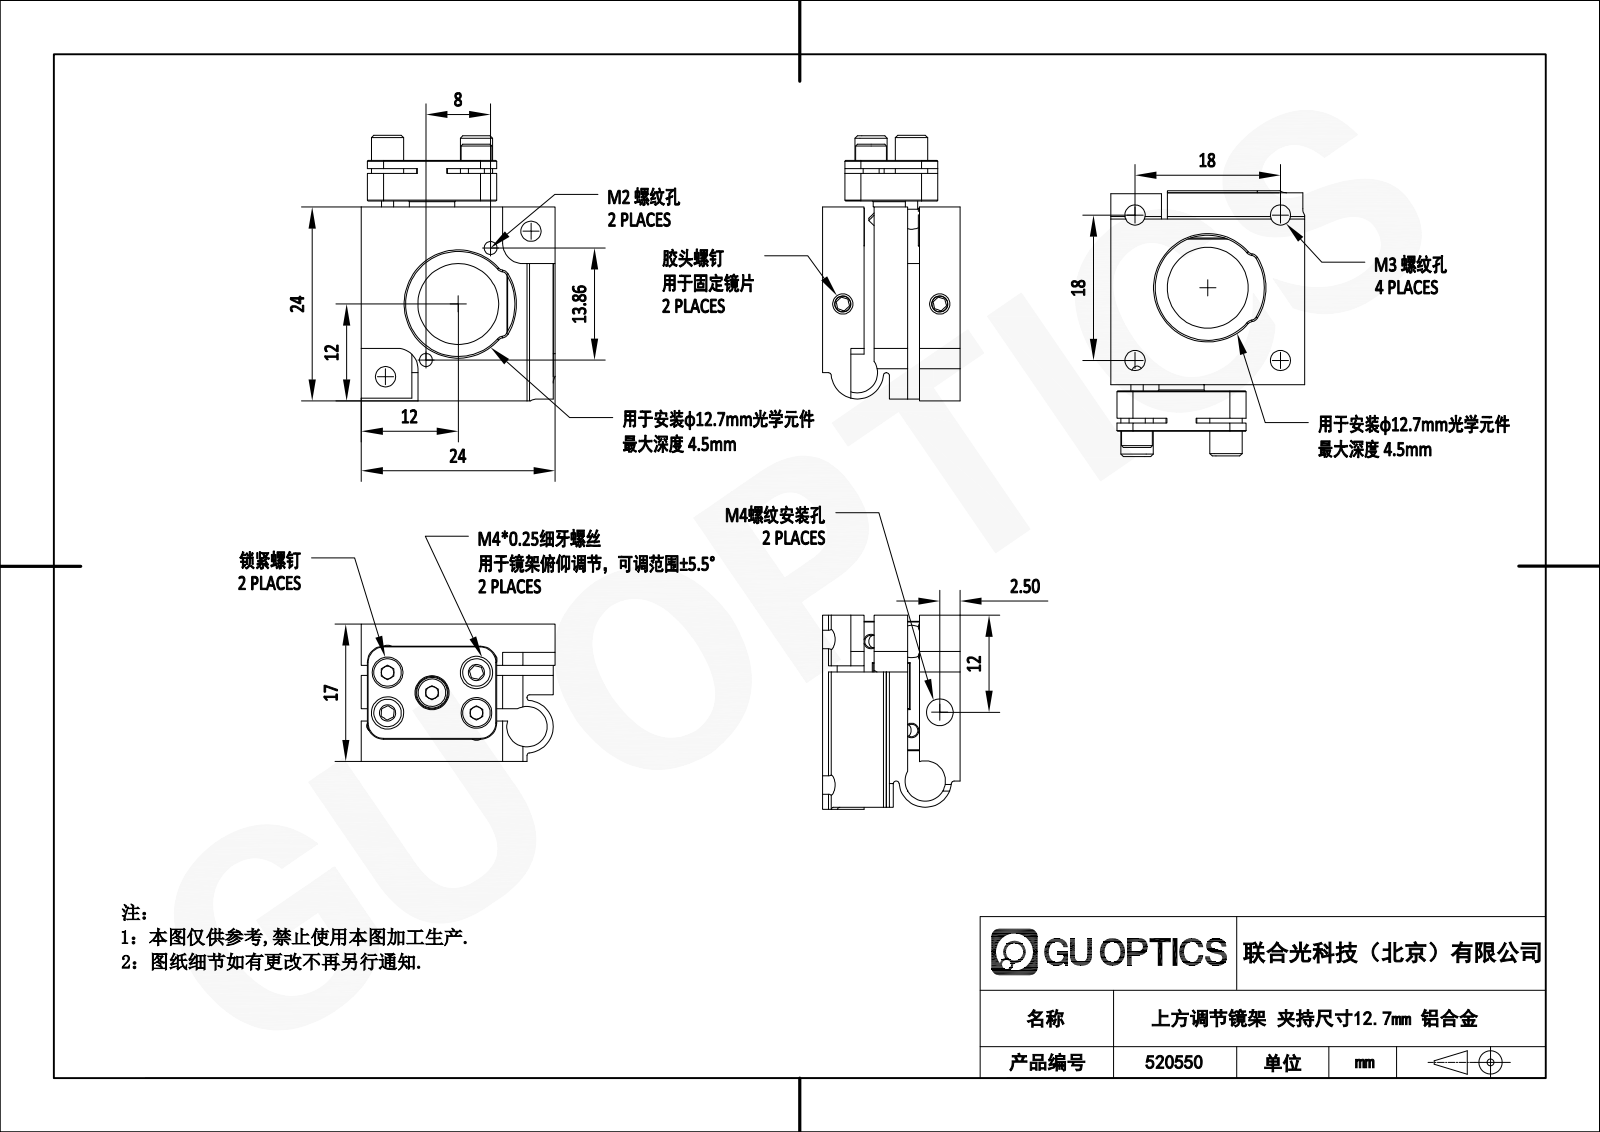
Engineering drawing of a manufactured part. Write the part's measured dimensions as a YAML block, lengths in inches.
part_name: "耳1.5 440C粣創詩埴翐种_33.2.25-DZ-耳1.5*5; 1.1.6.1.3_标准挠性光学调整架M4x0.25细牙螺丝，长度8mm，零部件; 30.1.圆柱头内六角不锈钢螺丝_30.1.18-M2*6; 30.1.圆柱头内六角不锈钢螺丝_30.1.16-M2*4 (+2 more)"
step_written_by: "SolidWorks 2021 (CONFIG_CONTROL_DESIGN)"
units: inches
bodies: {solids: 16, faces: 469, planar: 173, cylindrical: 168, other: 128}
overall_size: [1.294, 0.945, 0.63]
volume: 0.309
surface_area: 10.33
round_holes:
  - {diameter: 0.098, count: 6}
  - {diameter: 0.13, count: 4}
  - {diameter: 0.063, count: 3}
  - {diameter: 0.059, count: 2}
  - {diameter: 0.081, count: 2}
  - {diameter: 0.083, count: 2}
  - {diameter: 0.118, count: 2}
  - {diameter: 0.197, count: 2}
  - {diameter: 0.087, count: 1}
  - {diameter: 0.157, count: 1}
  - {diameter: 0.394, count: 1}
round_bosses_or_shafts:
  - {diameter: 0.079, count: 5}
  - {diameter: 0.059, count: 5}
  - {diameter: 0.15, count: 3}
  - {diameter: 0.157, count: 2}
  - {diameter: 0.118, count: 2}
partial_cylinders:
  - {radius: 0.014, count: 6}
  - {radius: 0.079, count: 6}
  - {radius: 0.03, count: 5}
  - {radius: 0.039, count: 3}
  - {radius: 0.059, count: 2}
  - {radius: 0.089, count: 2}
  - {radius: 0.098, count: 2}
  - {radius: 0.128, count: 2}
face_to_face_distances: [0.236, 0.453, 0.059, 0.63, 0.162, 0.394, 0.231, 0.177, 0.049, 0.221]
hole_center_spacings: [0.238, 0.501, 0.709, 0.095, 0.197, 0.213, 0.269, 0.315]
